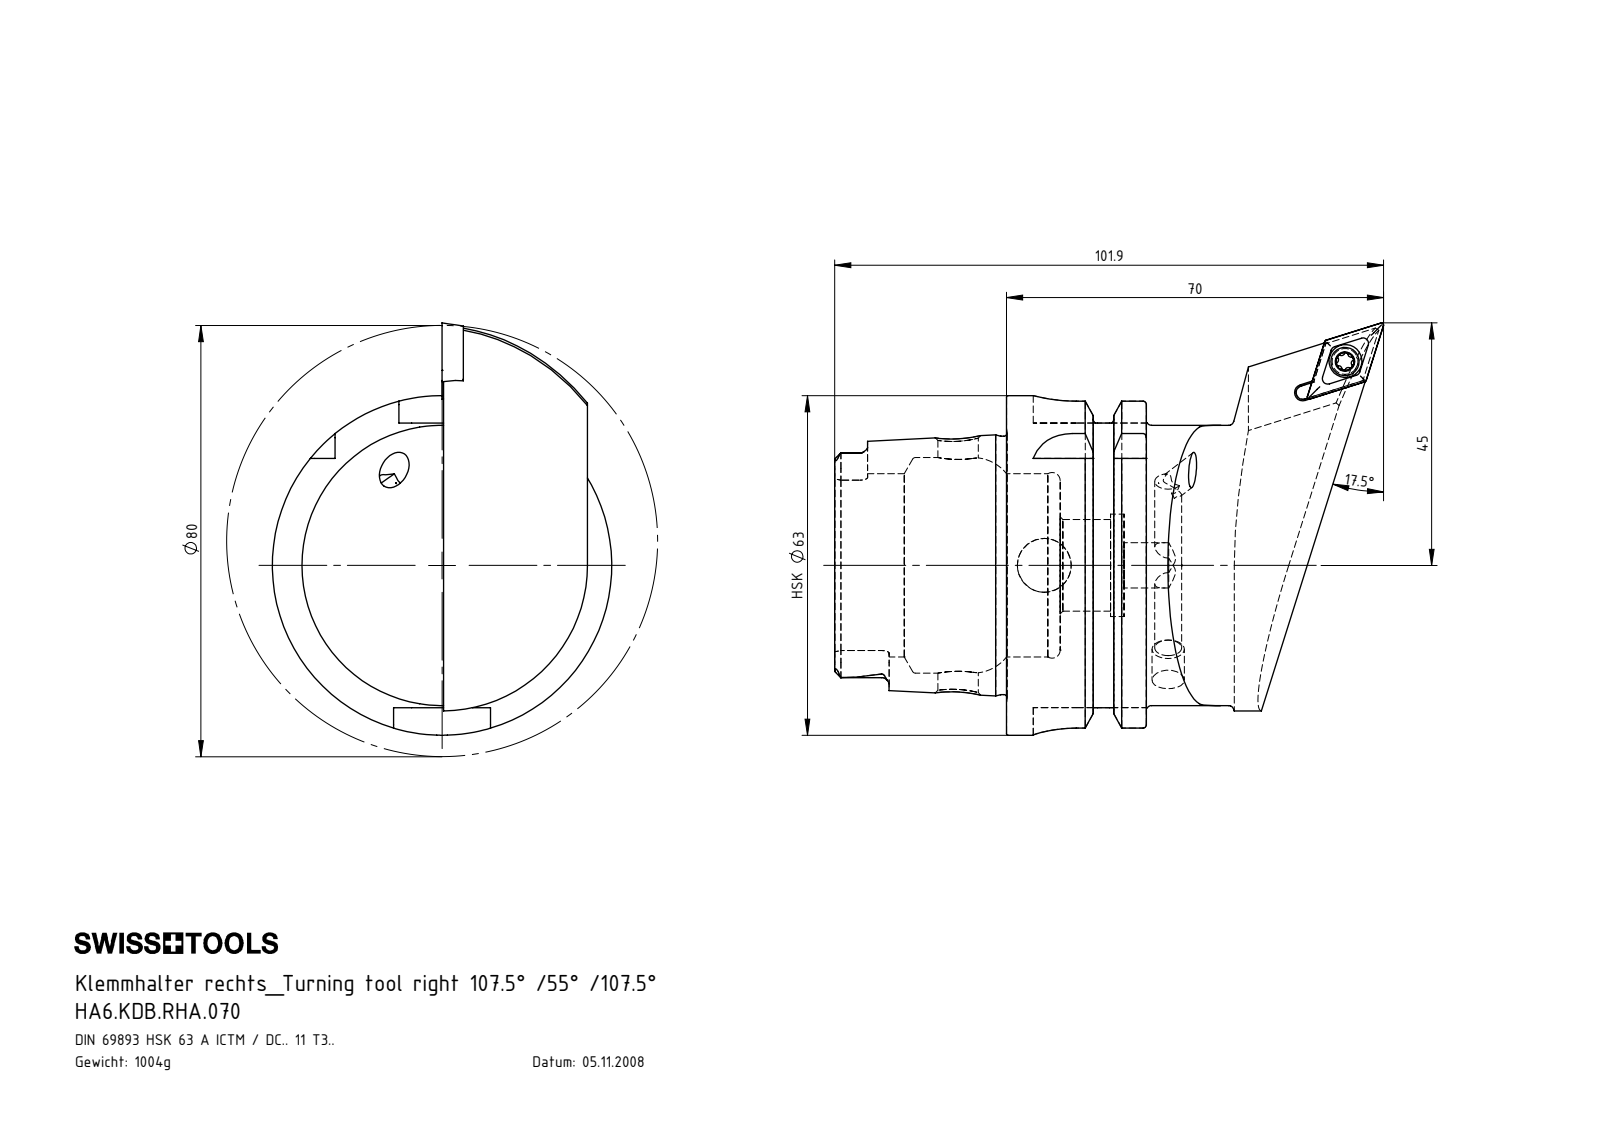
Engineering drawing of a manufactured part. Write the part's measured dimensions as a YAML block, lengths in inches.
part_name: "HA6-KDB.RHA.070; KVT_MB_600_050; WCB-ER2.001.009_A; DCMT11T304 (+1 more)"
step_written_by: "SolidWorks 2012 (CONFIG_CONTROL_DESIGN)"
units: inches
bodies: {solids: 5, faces: 313, planar: 77, cylindrical: 92, other: 144}
overall_size: [4.012, 3.012, 2.48]
volume: 7.899
surface_area: 45.85
round_holes:
  - {diameter: 0.165, count: 2}
  - {diameter: 0.13, count: 1}
  - {diameter: 0.157, count: 1}
  - {diameter: 0.173, count: 1}
  - {diameter: 0.197, count: 1}
  - {diameter: 0.24, count: 1}
  - {diameter: 0.295, count: 1}
  - {diameter: 0.331, count: 1}
  - {diameter: 0.394, count: 1}
  - {diameter: 0.669, count: 1}
  - {diameter: 0.748, count: 1}
  - {diameter: 1.339, count: 1}
round_bosses_or_shafts:
  - {diameter: 2.48, count: 1}
  - {diameter: 2.163, count: 1}
  - {diameter: 2.047, count: 1}
  - {diameter: 1.887, count: 1}
  - {diameter: 0.207, count: 1}
  - {diameter: 0.197, count: 1}
  - {diameter: 0.157, count: 1}
partial_cylinders:
  - {radius: 0.013, count: 6}
  - {radius: 0.023, count: 6}
  - {radius: 0.055, count: 6}
  - {radius: 0.315, count: 4}
  - {radius: 0.111, count: 2}
  - {radius: 0.113, count: 2}
  - {radius: 0.049, count: 1}
  - {radius: 0.236, count: 1}
face_to_face_distances: [1.022, 0.63, 0.392, 1.051, 1.256, 1.648, 2.278, 2.079, 0.858, 0.467]
hole_center_spacings: [2.655, 2.66]
